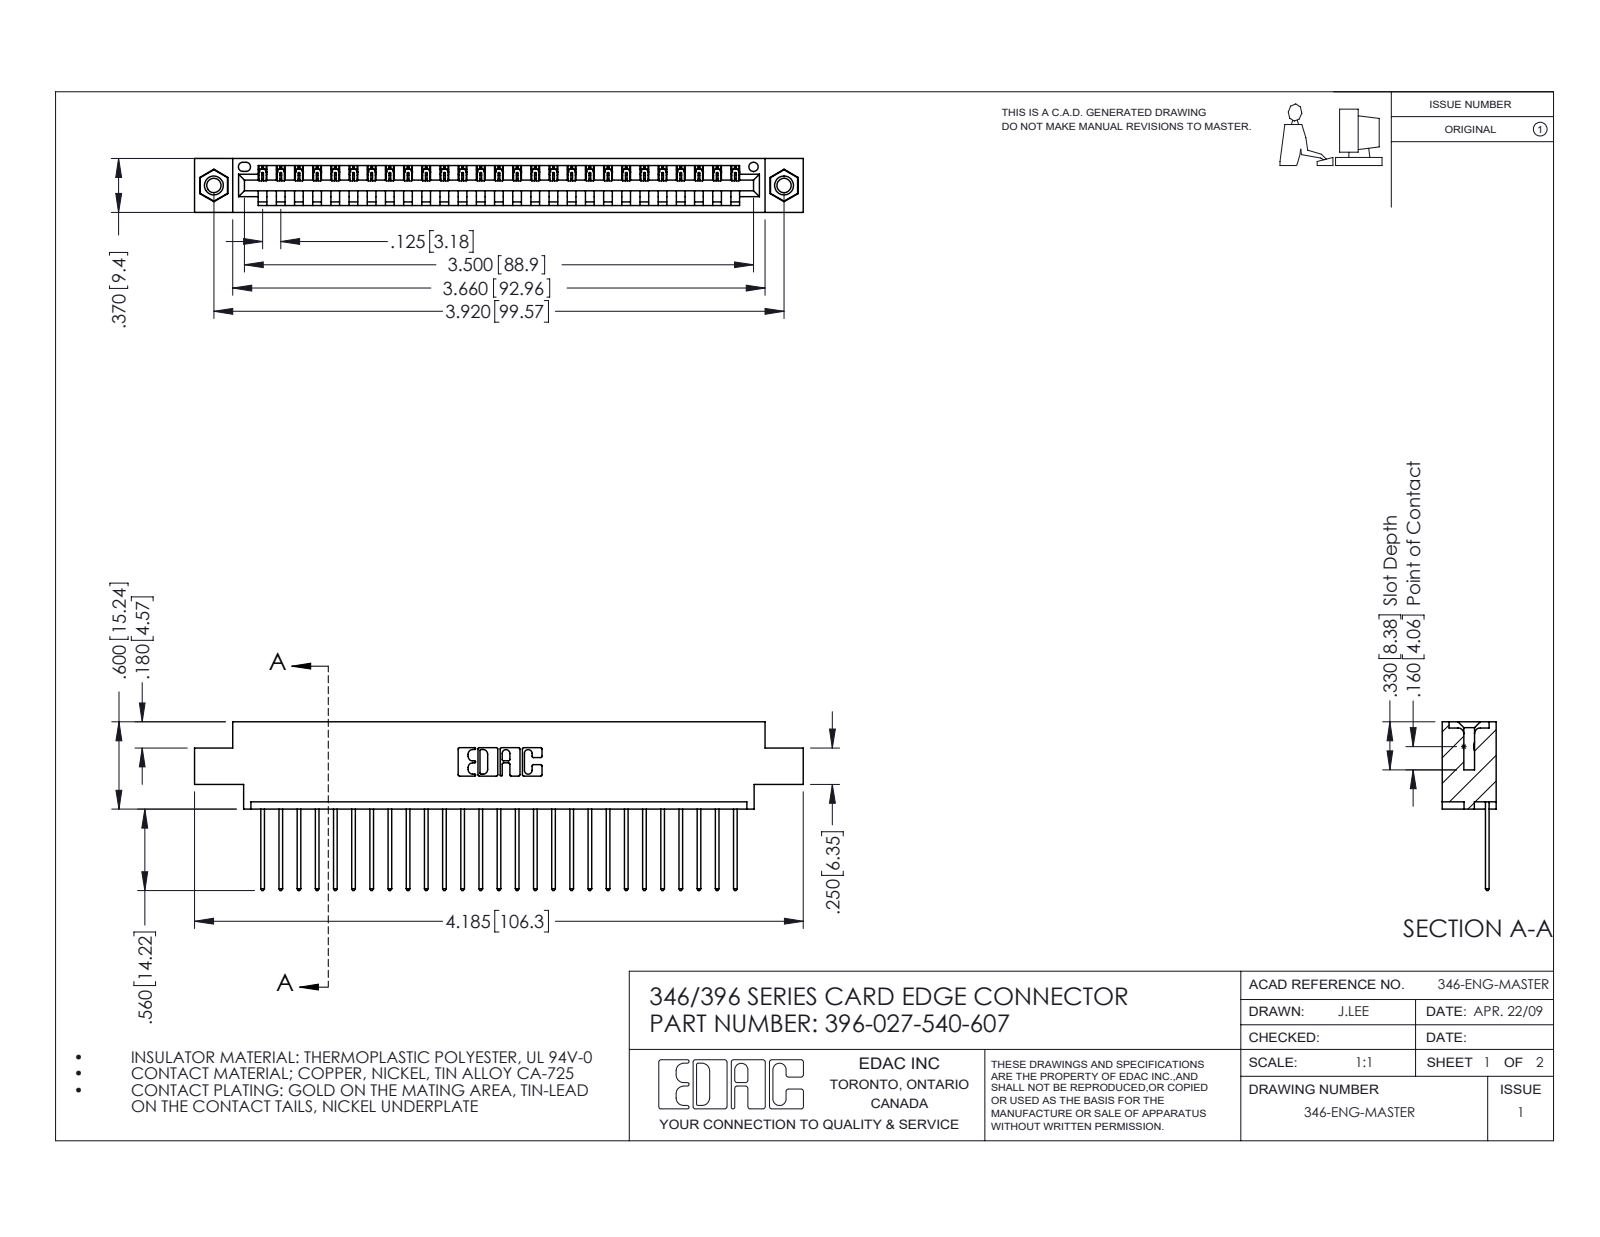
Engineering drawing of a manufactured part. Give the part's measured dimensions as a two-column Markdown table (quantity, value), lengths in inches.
| quantity | value |
| --- | --- |
| part name | 345-292-001_345-293-140; 396-027-540-607; 346 Part_0.170 Offset - 0.156 Dia-TI; 345-250-001_345-250-005-103 |
| STEP written by | SolidWorks 2016 (CONFIG_CONTROL_DESIGN) |
| units | inches |
| bodies | 30 solids, 1752 faces (1192 planar, 544 cylindrical, 16 other) |
| overall size | 4.185 × 1.16 × 0.37 |
| volume | 0.607 in³ |
| surface area | 19.72 in² |
| round holes (diameter × count) | 0.098 × 2, 0.125 × 2, 0.156 × 2, 0.064 × 1 |
| round bosses / shafts (diameter × count) | 0.155 × 2 |
| partial cylindrical surfaces (radius × count) | 0.006 × 54, 0.01 × 54, 0.01 × 22, 0.007 × 6, 0.031 × 6, 0.026 × 3, 0.031 × 2, 0.04 × 2 |
| main face-to-face distances | 0.048, 0.322, 0.37, 0.25, 0.072, 0.298, 0.025, 0.222, 0.148, 0.1 |
| hole center spacings | 0.246, 3.712, 3.92 |
